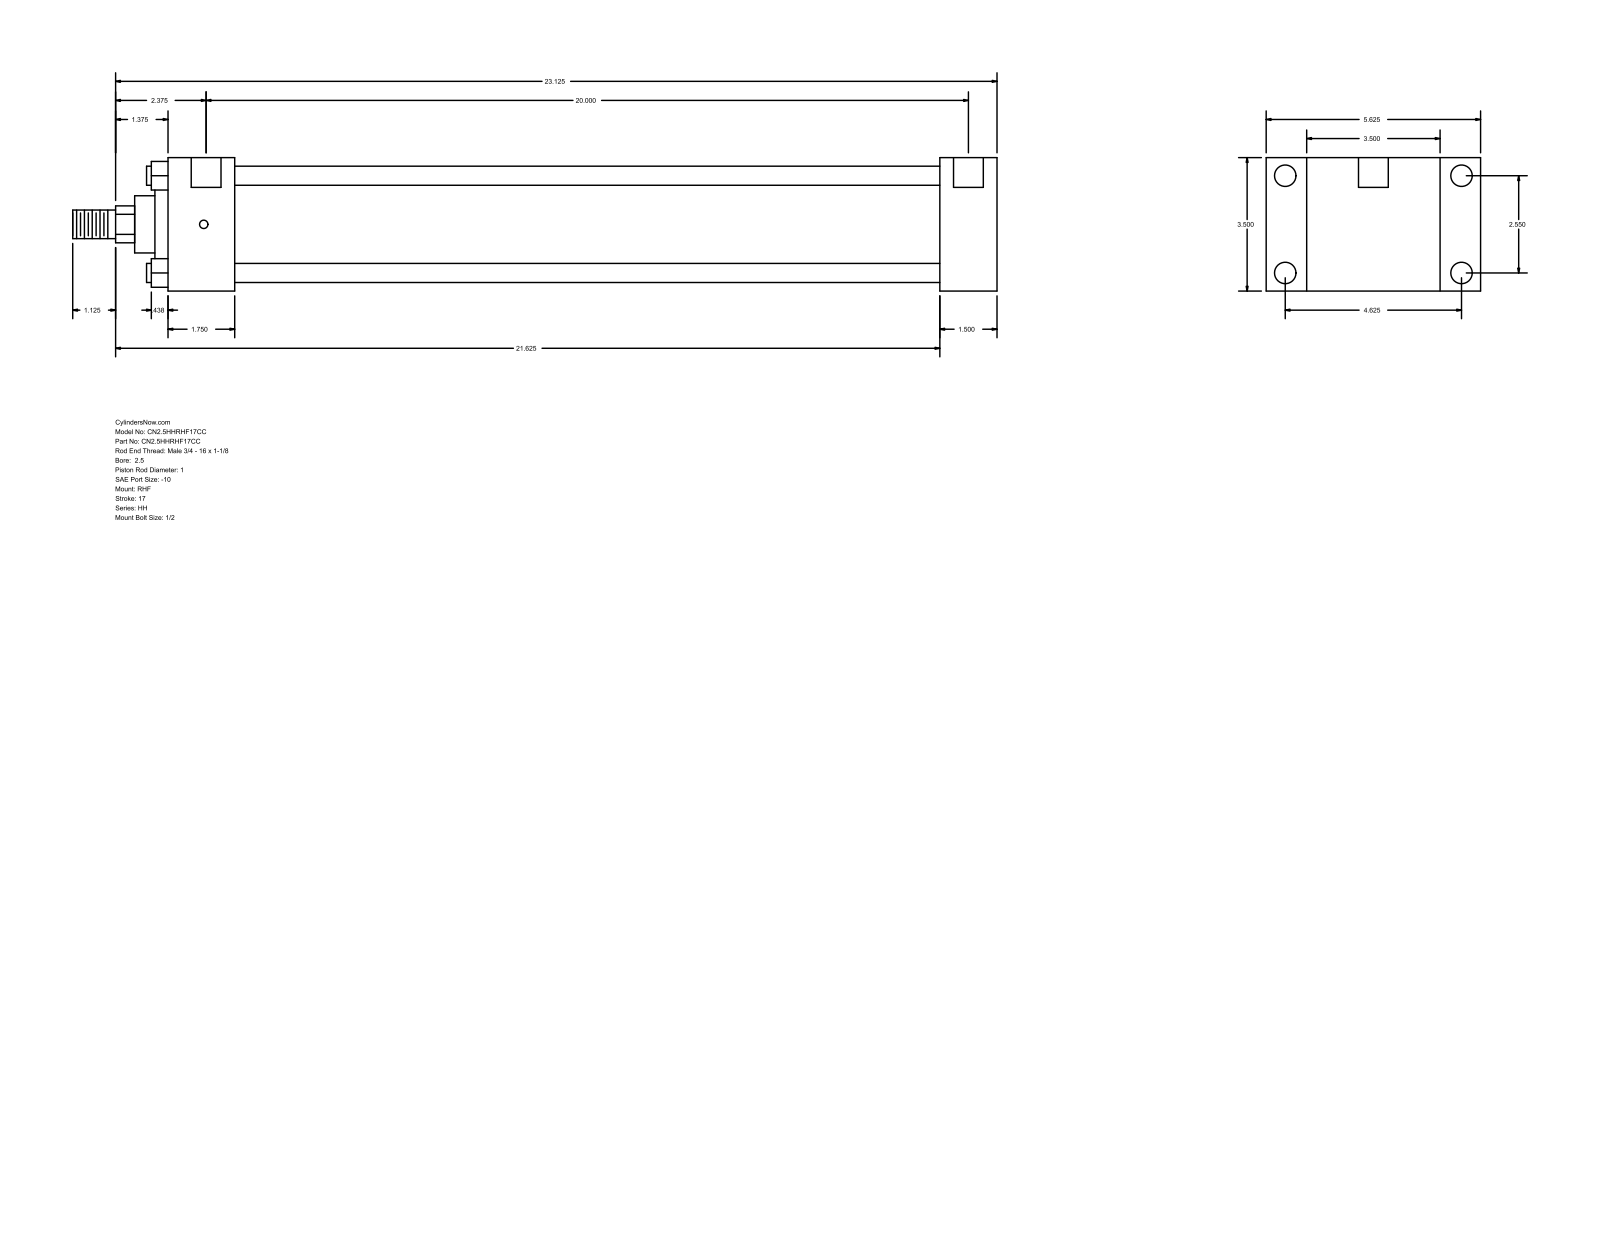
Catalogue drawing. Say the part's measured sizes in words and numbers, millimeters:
The part is named "HH_RHF__0250_1". Its 3-D file was written by "GSSL Pune (CONFIG_CONTROL_DESIGN)". It is 0 solids with 90 faces: 61 planar, 29 cylindrical and 0 other. Overall it measures 615.95 by 142.88 by 88.9 millimeters. Round holes: 4 of diameter 5.56, 4 of diameter 14.3, 2 of diameter 19.84. Round bosses or shafts: 4 of diameter 12.7, 1 of diameter 73.03, 1 of diameter 60.33, 1 of diameter 38.1, 1 of diameter 25.4, 1 of diameter 19.05. Partial cylindrical surfaces (rounded edges, fillets, slot ends): 1 of radius 12.29. The main face-to-face distances are 88.9, 38.11, 26.99, 115.89, 514.35, 552.46, 142.88, 44.46, 469.89, 508. The hole center spacings are 64.76, 117.48, 134.15, 511.17, 1.58, 1.59, 508, 509.58.
